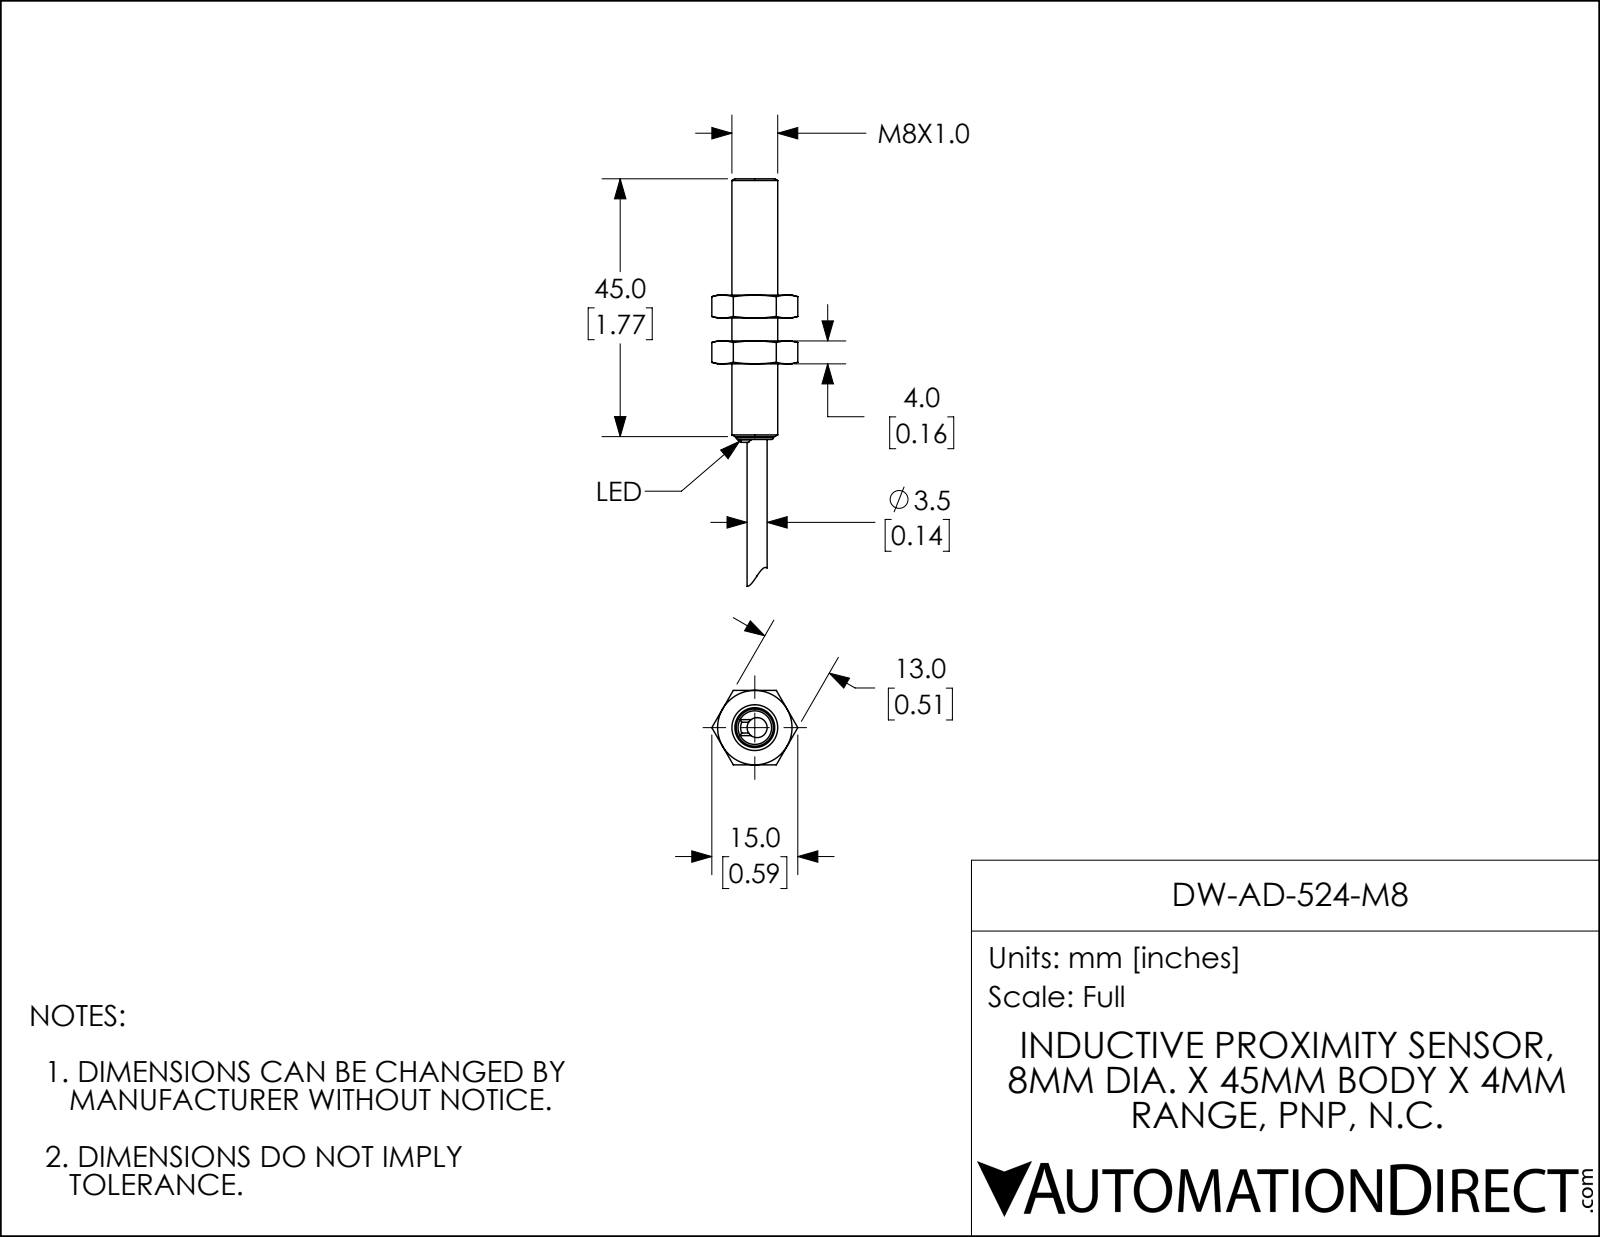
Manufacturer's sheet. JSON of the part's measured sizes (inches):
{"part_name": "DW-AD-50x-M8", "step_written_by": "SolidWorks 2017 (AUTOMOTIVE_DESIGN)", "units": "inches", "bodies": {"solids": 1, "faces": 19, "planar": 9, "cylindrical": 4, "other": 6}, "overall_size": [2.801, 0.315, 0.315], "volume_in3": 0.167, "surface_area_in2": 2.508, "round_bosses_or_shafts": [[0.315, 1], [0.256, 1], [0.197, 1]], "partial_cylinders_radius": [[0.115, 1]], "face_to_face_distances": [0.02, 1.787, 1.768, 1.772, 1.791, 1.811, 1.807, 0.039, 0.11]}
